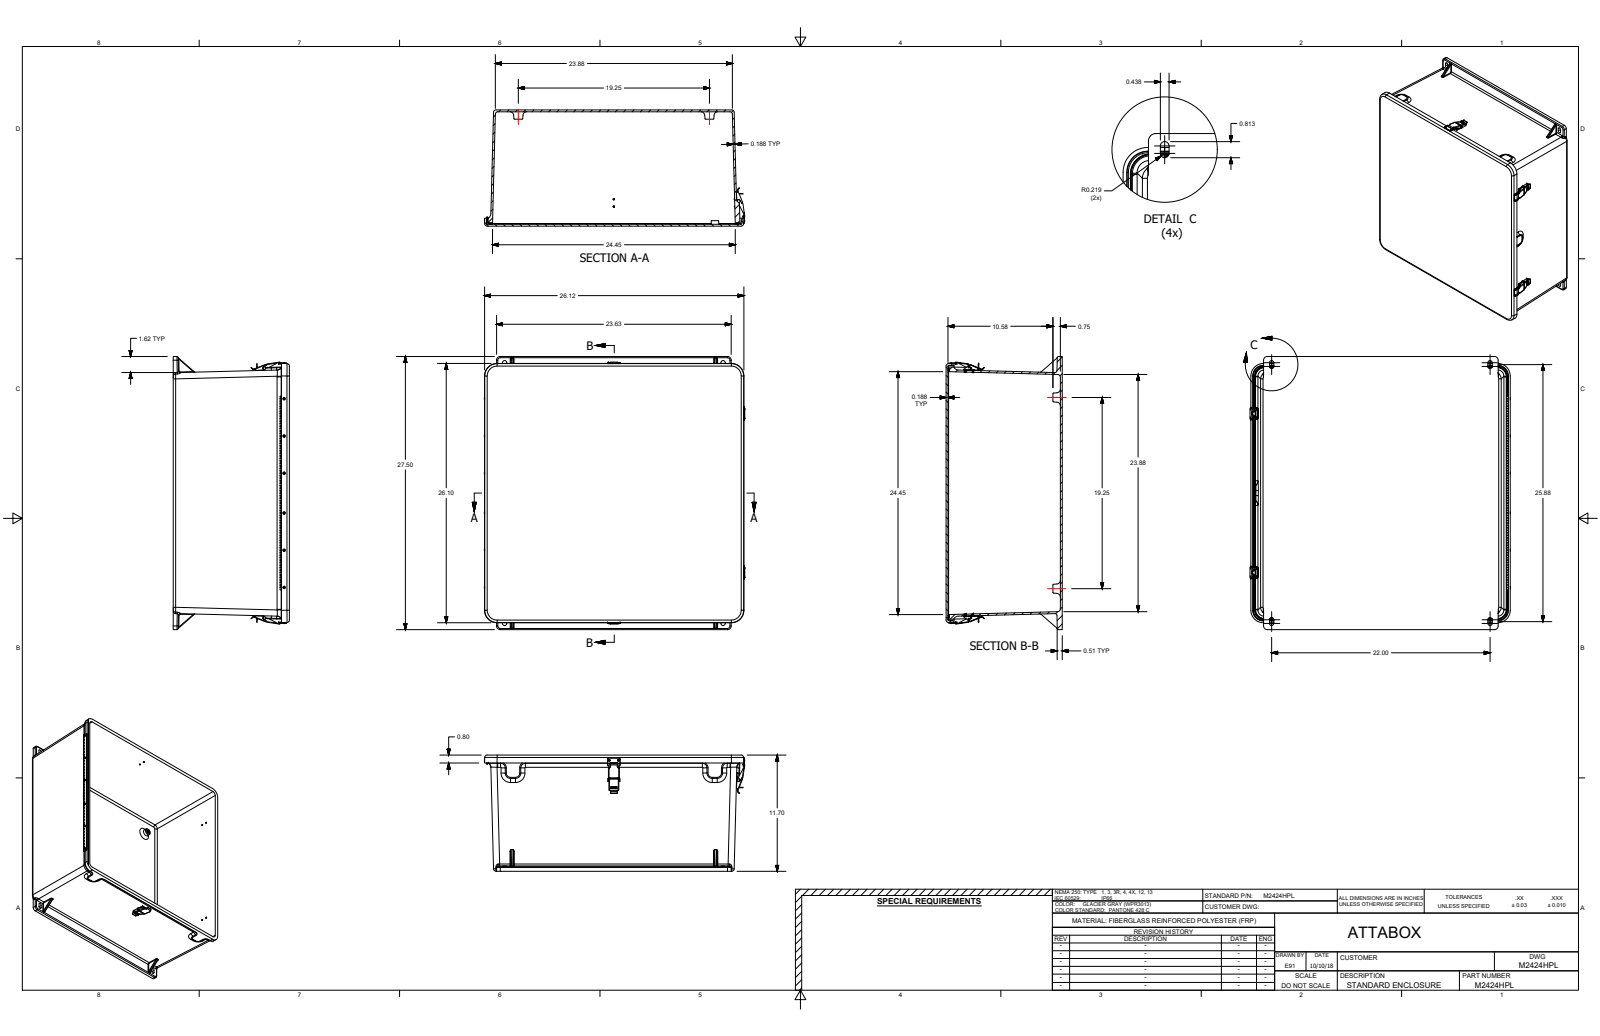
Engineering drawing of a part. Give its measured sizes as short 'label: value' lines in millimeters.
name: M2424HPL
written by: SolidWorks 2018 (AUTOMOTIVE_DESIGN)
unit: mm
bodies: 62 solids, 2139 faces (803 planar, 878 cylindrical, 458 other)
size: 698.5 × 666.1 × 297.2
volume: 8 625 000 mm³; area: 3 408 000 mm²
holes: 28× ⌀2.6, 24× ⌀3.5, 12× ⌀3.3, 8× ⌀3.3, 8× ⌀3.6, 6× ⌀3.4, 4× ⌀5.2, 4× ⌀9.5, 4× ⌀9.9, 3× ⌀3.4, 2× ⌀7.9, 1× ⌀2.2
bosses: 19× ⌀3.2, 9× ⌀3.2, 3× ⌀7.6, 3× ⌀4.3, 3× ⌀3, 1× ⌀3.9, 1× ⌀2.2
rounds: 72× R0.1, 44× R0.4, 40× R3.2, 35× R0.5, 32× R1.1, 30× R1.5, 24× R0.8, 17× R12.7
face distances: 4.8, 292.4, 297.2, 287.7, 4.8, 641.7, 12, 290.5, 285.8, 1.9
hole spacings: 95.3, 190.5, 406.4, 279.4, 292.1, 0.3, 22.8, 184.2
